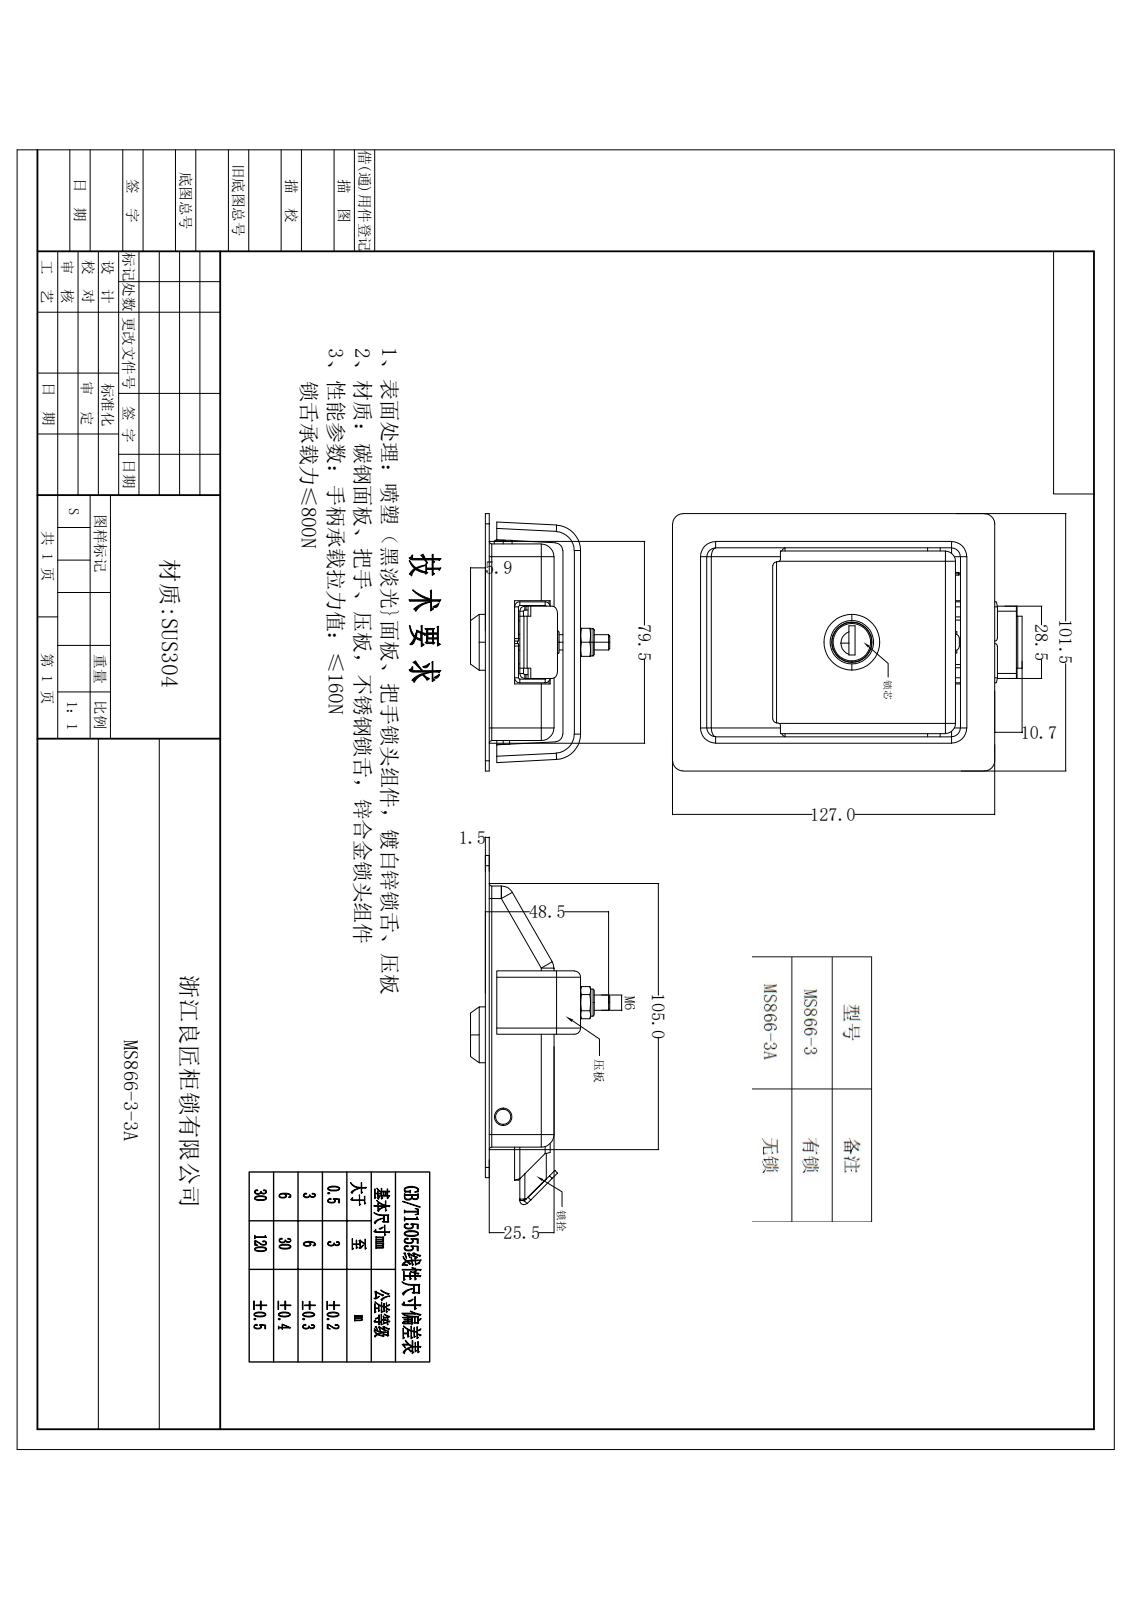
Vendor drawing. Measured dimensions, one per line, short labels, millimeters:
written by: Rhino 8.5 (CONFIG_CONTROL_DESIGN)
unit: mm
bodies: 17 solids, 566 faces (251 planar, 189 cylindrical, 126 other)
size: 137.72 × 101.5 × 54.9
volume: 52 792 mm³; area: 77 175 mm²
holes: 1× ⌀4, 1× ⌀5, 1× ⌀5.1, 1× ⌀5.9, 1× ⌀6.1, 1× ⌀6.4, 1× ⌀15.2, 1× ⌀15.9
bosses: 1× ⌀22, 1× ⌀18, 1× ⌀15.8, 1× ⌀12, 1× ⌀10.7, 1× ⌀9, 1× ⌀7, 1× ⌀6
rounds: 21× R1, 14× R5, 12× R0.5, 11× R2.5, 11× R3.5, 8× R1.5, 7× R2, 7× R4
face distances: 1.5, 25.5, 24, 27, 2.75, 73.25, 10.5, 12, 76, 36
hole spacings: 12.7
